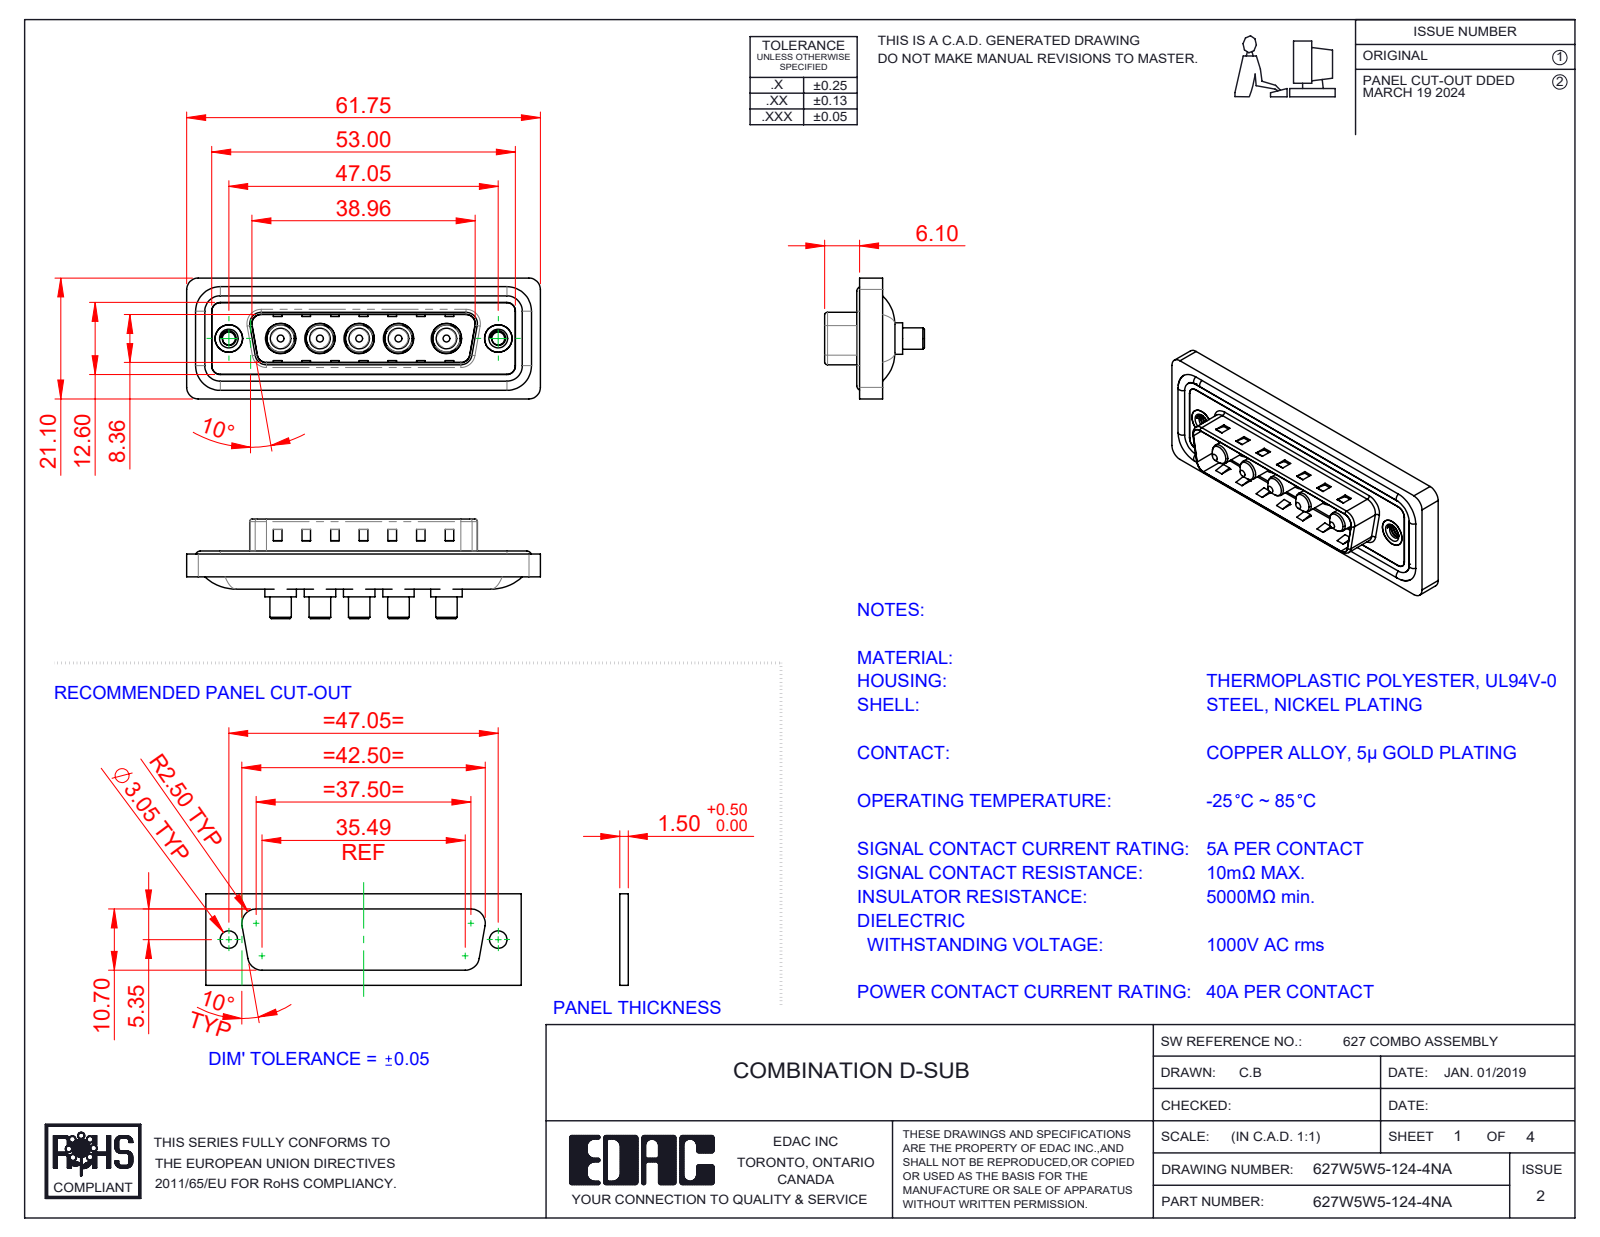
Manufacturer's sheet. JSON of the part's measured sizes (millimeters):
{"part_name": "627Combo Threaded Rivet_A; 627W5W5-124-4NA; 627Combo Housing_5W5; 627Combo Waterproof Housing_25 Contacts (+3 more)", "step_written_by": "SolidWorks 2023 (CONFIG_CONTROL_DESIGN)", "units": "millimeters", "bodies": {"solids": 17, "faces": 676, "planar": 259, "cylindrical": 285, "other": 132}, "overall_size": [61.75, 21.1, 17.4], "volume_mm3": 7567, "surface_area_mm2": 11848, "round_holes": [[4.85, 5], [5.3, 5], [2.26, 2], [4, 2], [4.8, 2], [5, 2]], "round_bosses_or_shafts": [[5.5, 5], [5.2, 5], [4.75, 5], [3.75, 5], [3.6, 5], [1.6, 4], [4.9, 2]], "partial_cylinders_radius": [[1.5, 22], [2, 18], [0.5, 8], [1.6, 8], [2.1, 5], [0.25, 4], [0.6, 4], [0.65, 4]], "face_to_face_distances": [0.4, 1.5, 0.5, 1.1, 3.1, 1.6, 2.9, 0.82, 9.58, 5.65], "hole_center_spacings": [6.86, 9.04, 13.73, 38.01, 6.87, 8.37, 8.38, 9.05]}
